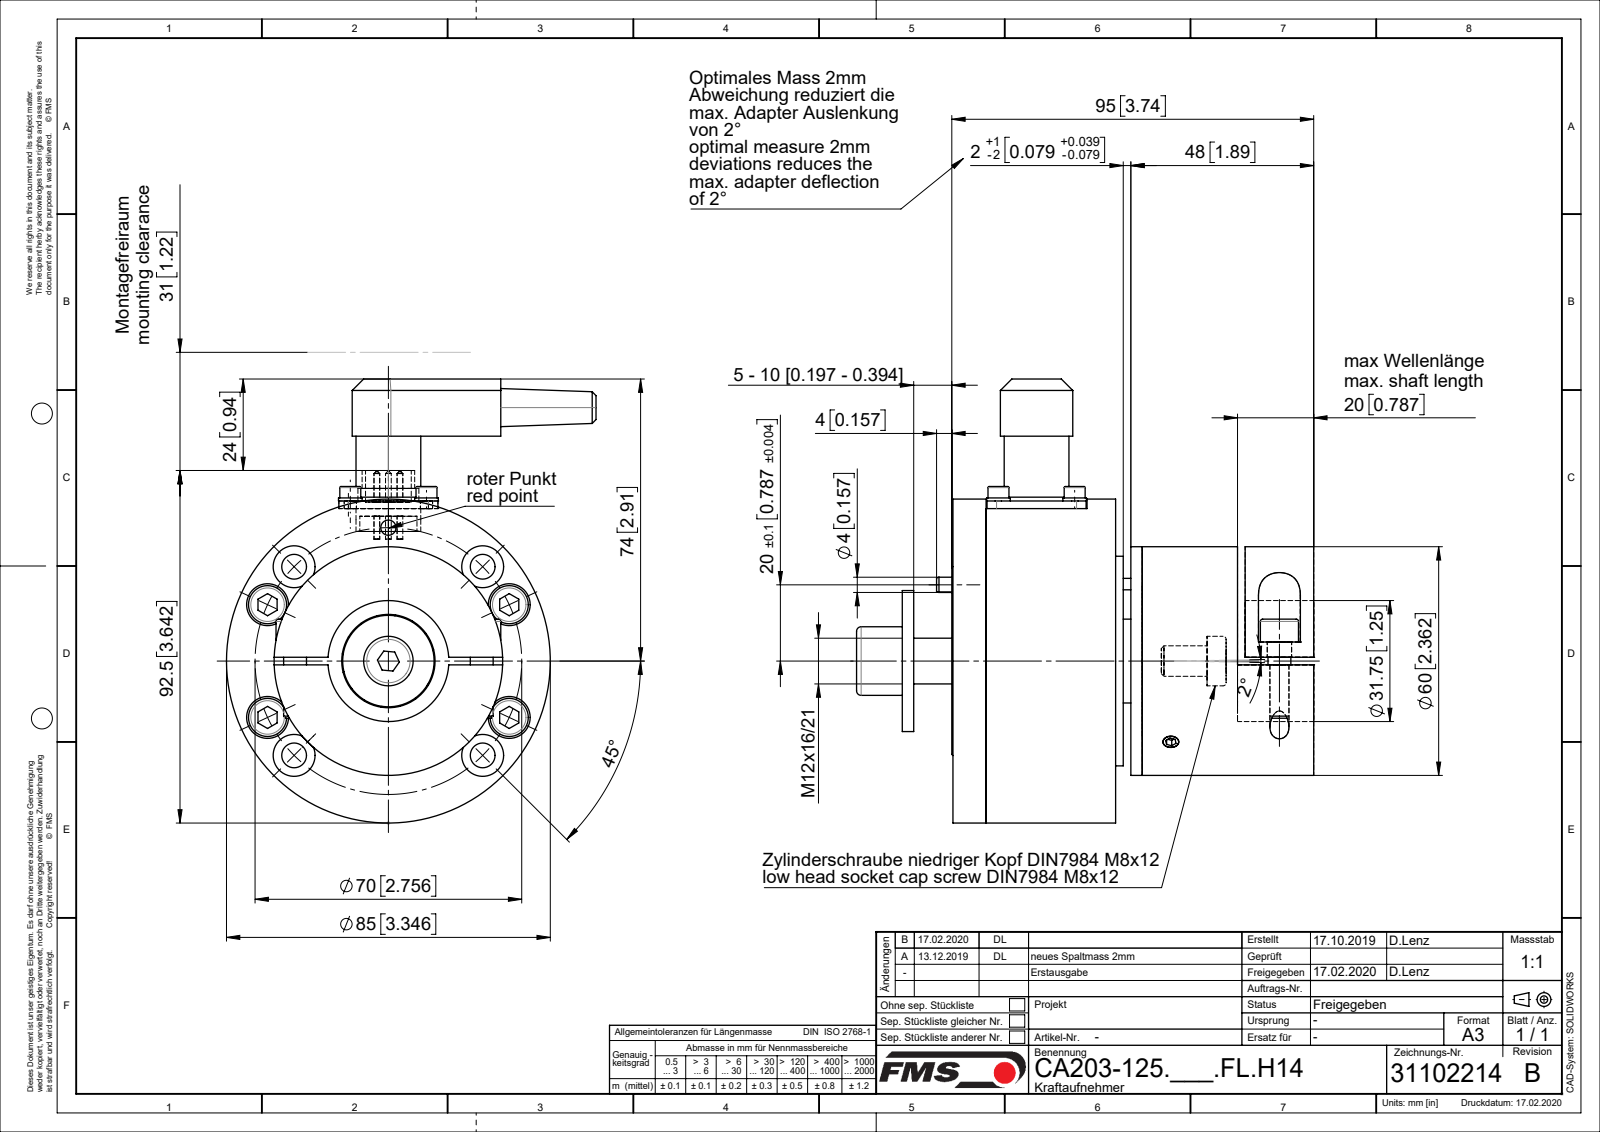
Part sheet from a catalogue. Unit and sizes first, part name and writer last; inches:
Units: inches
Overall size (bounding box): 4.744 × 4.587 × 3.819
Round holes (diameter × count): ⌀0.102 ×8, ⌀0.256 ×8, ⌀0.433 ×8, ⌀0.203 ×6, ⌀0.079 ×5, ⌀0.126 ×4, ⌀0.142 ×4, ⌀0.157 ×4, ⌀0.276 ×4, ⌀0.252 ×2, ⌀0.118 ×1, ⌀0.17 ×1
Round bosses / shafts (diameter × count): ⌀0.236 ×10, ⌀0.118 ×8, ⌀0.394 ×6, ⌀0.059 ×5, ⌀0.244 ×4, ⌀0.217 ×4, ⌀0.197 ×4, ⌀3.346 ×1
Partial cylindrical surfaces — rounded edges, fillets, slot ends (radius × count): R0.098 ×4, R0.197 ×2, R0.217 ×2, R0.374 ×1
Main face-to-face distances: 1.772, 1.949, 0.354, 0.453, 0.079, 1.24, 0.394, 1.693, 0.059, 1.594
Hole centre spacings: 0.787, 0.976, 0.992, 1.291, 1.378, 2.013, 2.223, 0.236
Volume: 19.43 in³ · Surface area: 174.3 in²
Bodies: 37 solids, 685 faces (229 planar, 315 cylindrical, 141 other)
Part name (STEP PRODUCT): C0705311_DI125; C0709081; C0612056; C0709072 (+8 more)
STEP written by: Mechanical Desktop 2009 (CONFIG_CONTROL_DESIGN)
